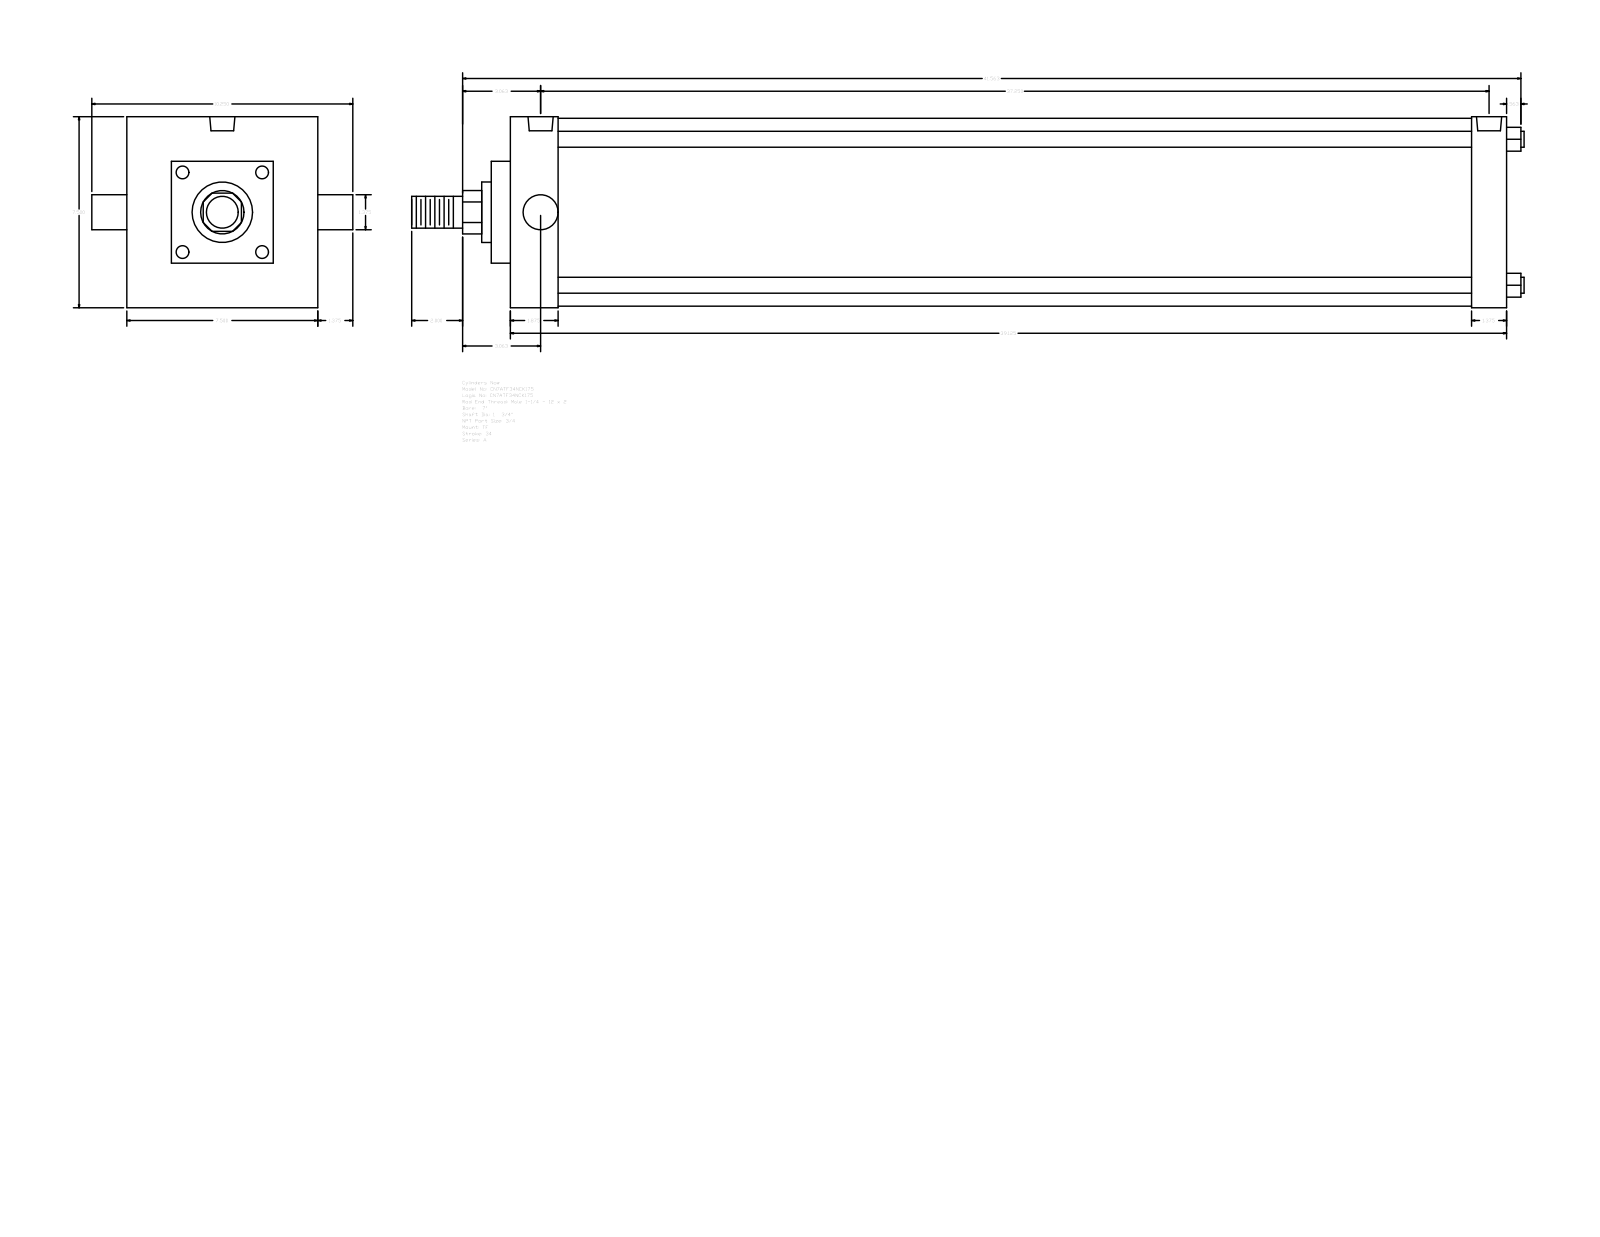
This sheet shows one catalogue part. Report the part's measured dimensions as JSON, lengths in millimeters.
{"part_name": "A_TF__0700_1.75", "step_written_by": "GSSL Pune (CONFIG_CONTROL_DESIGN)", "units": "millimeters", "bodies": {"solids": 0, "faces": 89, "planar": 65, "cylindrical": 24, "other": 0}, "overall_size": [1109.66, 260.35, 190.5], "round_holes": [[15.08, 3], [25.12, 2]], "round_bosses_or_shafts": [[15.88, 4], [187.32, 1], [60.33, 1], [44.45, 1], [34.92, 1], [31.75, 1]], "partial_cylinders_radius": [[21.63, 1]], "face_to_face_distances": [190.5, 993.78, 146.05, 19.05, 47.63, 946.15, 958.86, 911.23, 34.92, 44.45], "hole_center_spacings": [5.56, 940.59, 935.03, 946.15]}
